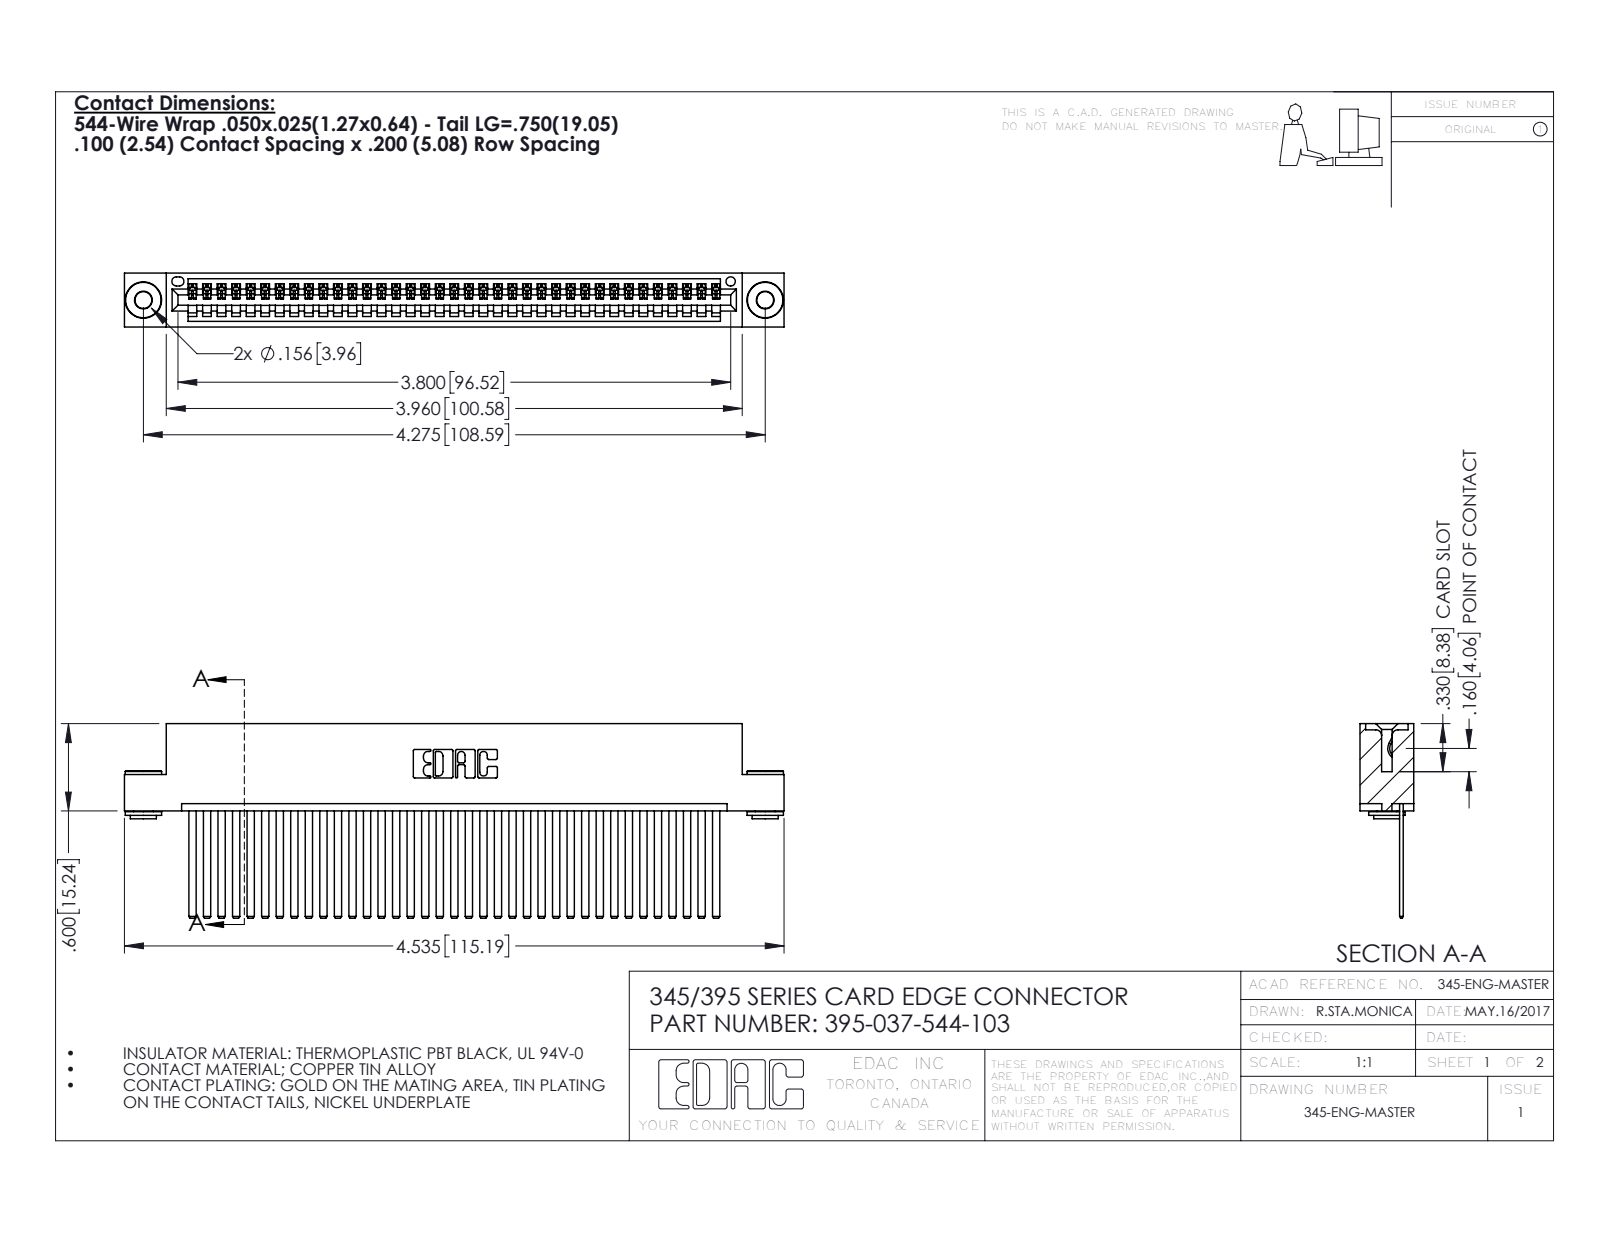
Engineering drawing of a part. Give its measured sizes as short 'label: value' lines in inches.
name: 345-250-002_345-250-002-102; 345-292-001_345-293-144; 395-037-544-103; 345 Part_Flush Mounting Lugs - 0.156 Dia-TH
written by: SolidWorks 2016 (CONFIG_CONTROL_DESIGN)
unit: in
bodies: 40 solids, 2088 faces (1422 planar, 658 cylindrical, 8 other)
size: 4.535 × 1.337 × 0.37
volume: 0.692 in³; area: 25.6 in²
holes: 2× ⌀0.116, 2× ⌀0.156, 1× ⌀0.064
bosses: 2× ⌀0.25, 2× ⌀0.18, 2× ⌀0.136
rounds: 74× R0.006, 22× R0.01, 6× R0.007, 6× R0.031, 3× R0.026, 2× R0.031, 2× R0.04, 1× R0.014
face distances: 0.072, 0.298, 0.025, 0.098, 0.272, 0.2, 0.37, 0.225, 0.149, 0.072
hole spacings: 0.27, 4.039, 4.275
